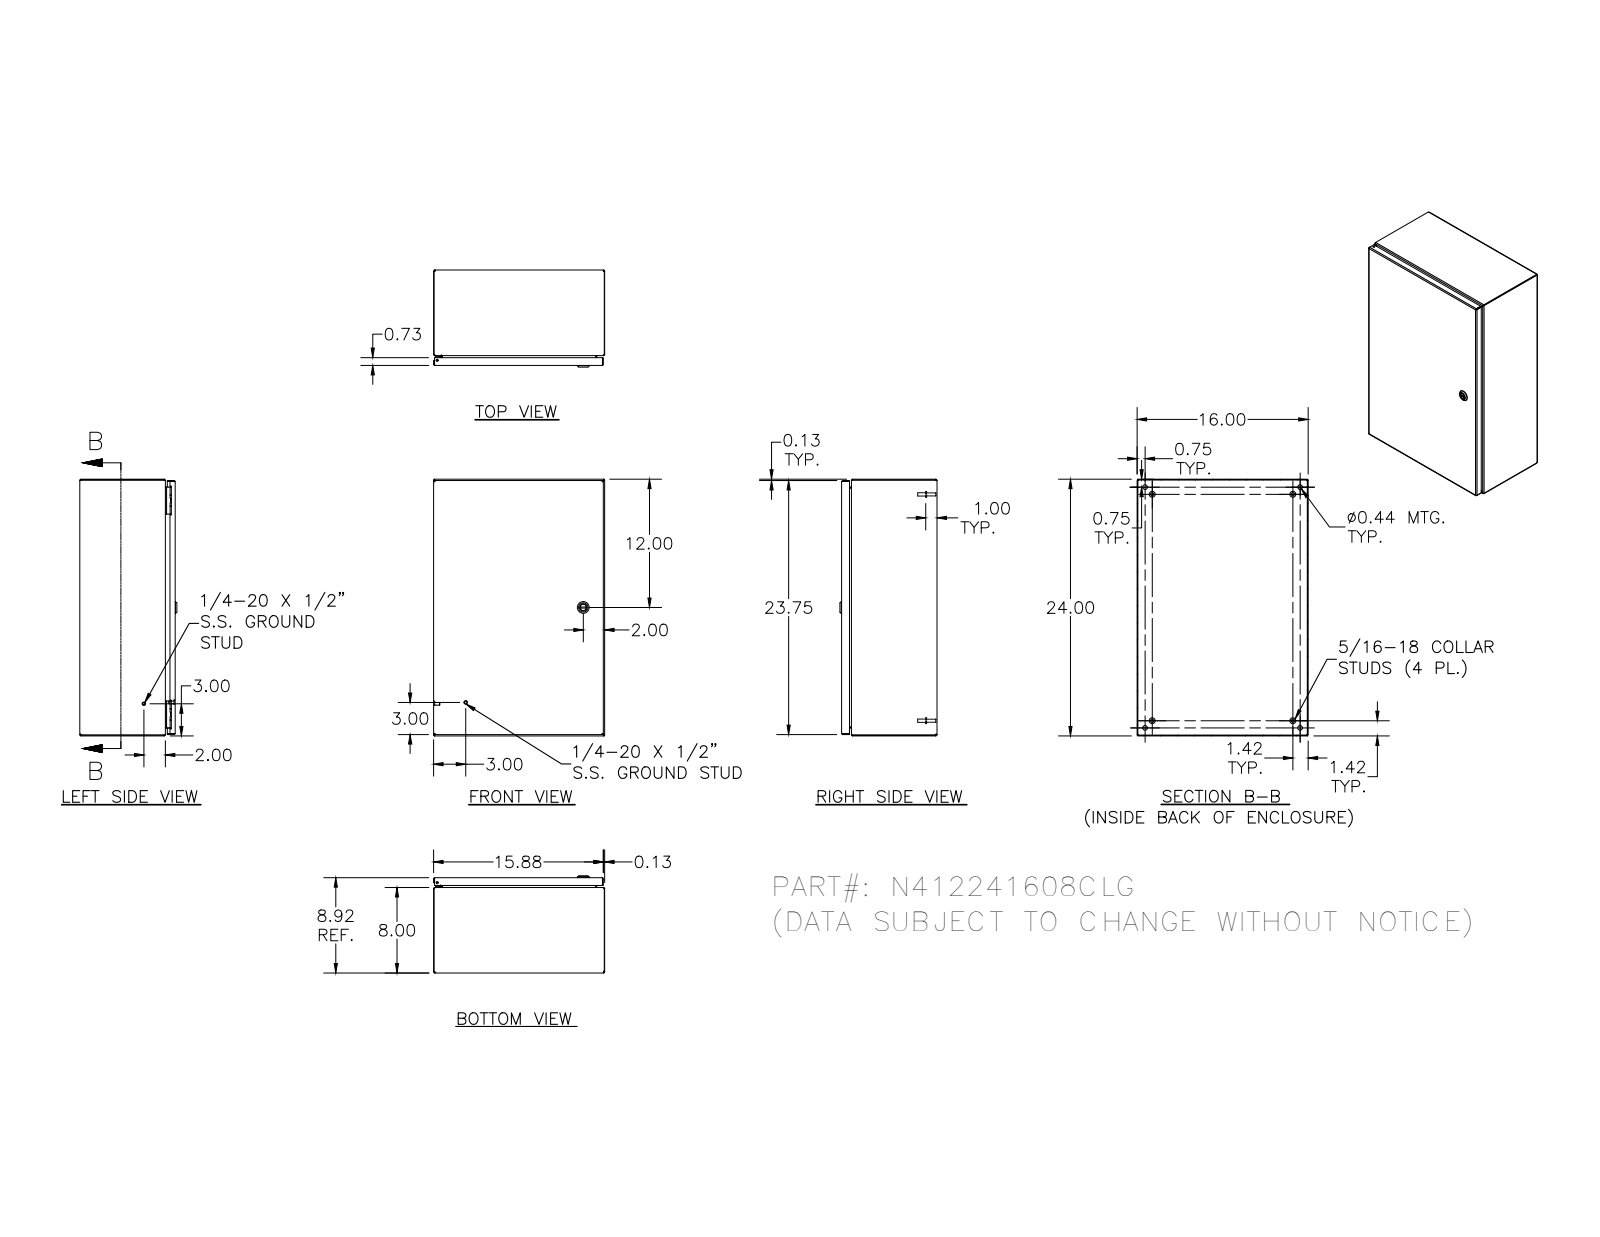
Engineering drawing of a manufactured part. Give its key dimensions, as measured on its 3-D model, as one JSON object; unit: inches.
{"part_name": "N412241608CLG", "step_written_by": "SolidWorks 2018 (AUTOMOTIVE_DESIGN)", "units": "inches", "bodies": {"solids": 33, "faces": 1449, "planar": 530, "cylindrical": 547, "other": 372}, "overall_size": [24, 16, 9.075], "volume_in3": 116.2, "surface_area_in2": 3160, "round_holes": [[0.188, 5], [0.093, 4], [0.152, 4], [0.167, 4], [0.172, 4], [0.437, 4], [0.156, 2], [0.187, 1], [0.197, 1], [0.315, 1], [0.394, 1], [0.402, 1]], "round_bosses_or_shafts": [[0.25, 10], [0.563, 4], [0.36, 4], [0.32, 4], [0.3, 4], [0.256, 4], [0.164, 4], [0.131, 4]], "partial_cylinders_radius": [[0.012, 30], [0.031, 30], [0.05, 26], [0.105, 20], [0.016, 18], [0.125, 16], [0.02, 13], [0.032, 8]], "face_to_face_distances": [0.074, 8.843, 8.769, 8.917, 0.074, 15.926, 16, 15.852, 15.926, 23.926], "hole_center_spacings": [20, 0.66, 0.656, 1.307, 1.965, 0.5, 0.984, 1.311]}
